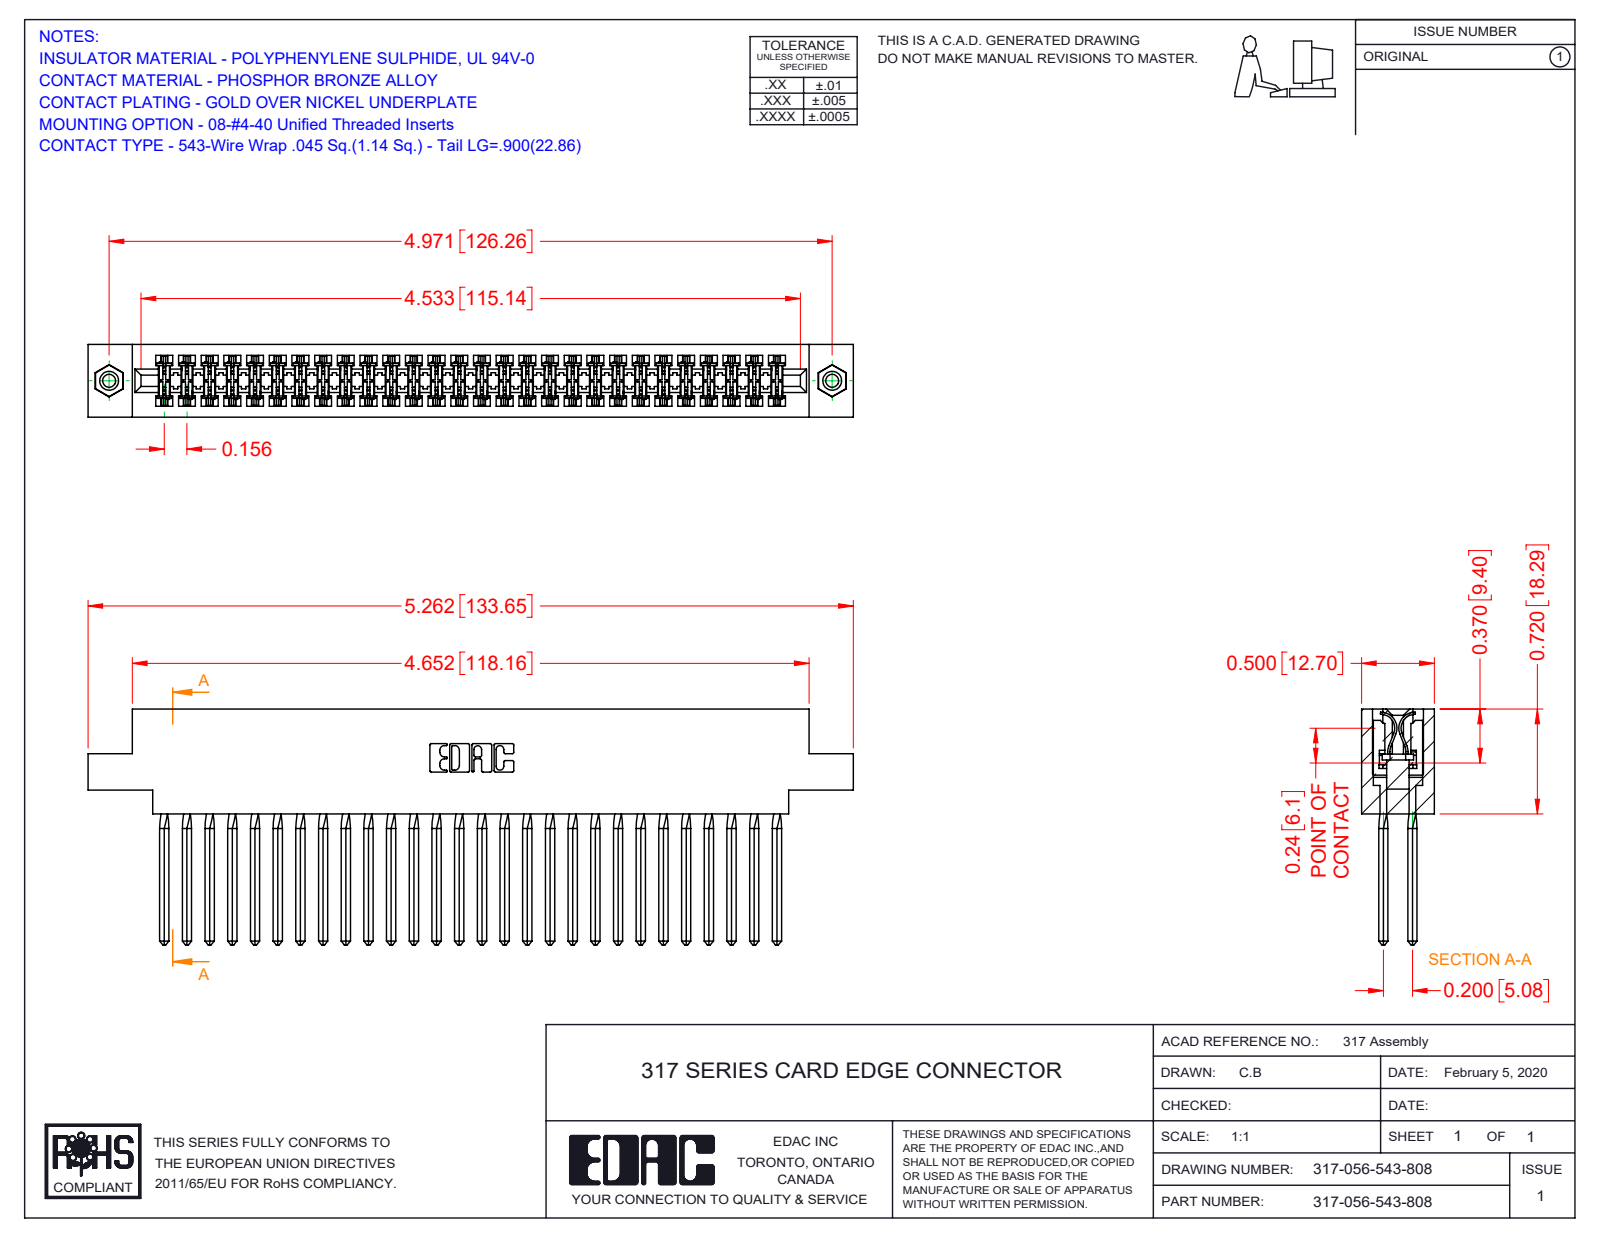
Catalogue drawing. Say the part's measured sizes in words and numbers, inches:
The part is named "317-056-543-878; 345-250-001_345-250-003-102; 317 Part_.156 Dia - TI; 317-290-001_543". Its 3-D file was written by "SolidWorks 2016 (CONFIG_CONTROL_DESIGN)". It is 59 solids with 5146 faces: 4178 planar, 728 cylindrical and 240 other. Overall it measures 5.262 by 1.62 by 0.5 inches. Its volume is 1.357 cubic inches and its surface area 51.45 square inches. Round holes: 2 of diameter 0.089, 2 of diameter 0.125, 2 of diameter 0.156. Round bosses or shafts: 2 of diameter 0.155. Partial cylindrical surfaces (rounded edges, fillets, slot ends): 112 of radius 0.015, 22 of radius 0.01, 6 of radius 0.007, 6 of radius 0.031, 3 of radius 0.026, 2 of radius 0.095, 2 of radius 0.1, 2 of radius 0.11. The main face-to-face distances are 0.5, 0.075, 0.425, 0.35, 0.11, 0.195, 0.094, 0.2, 0.72, 0.115. The hole center spacings are 4.971.
